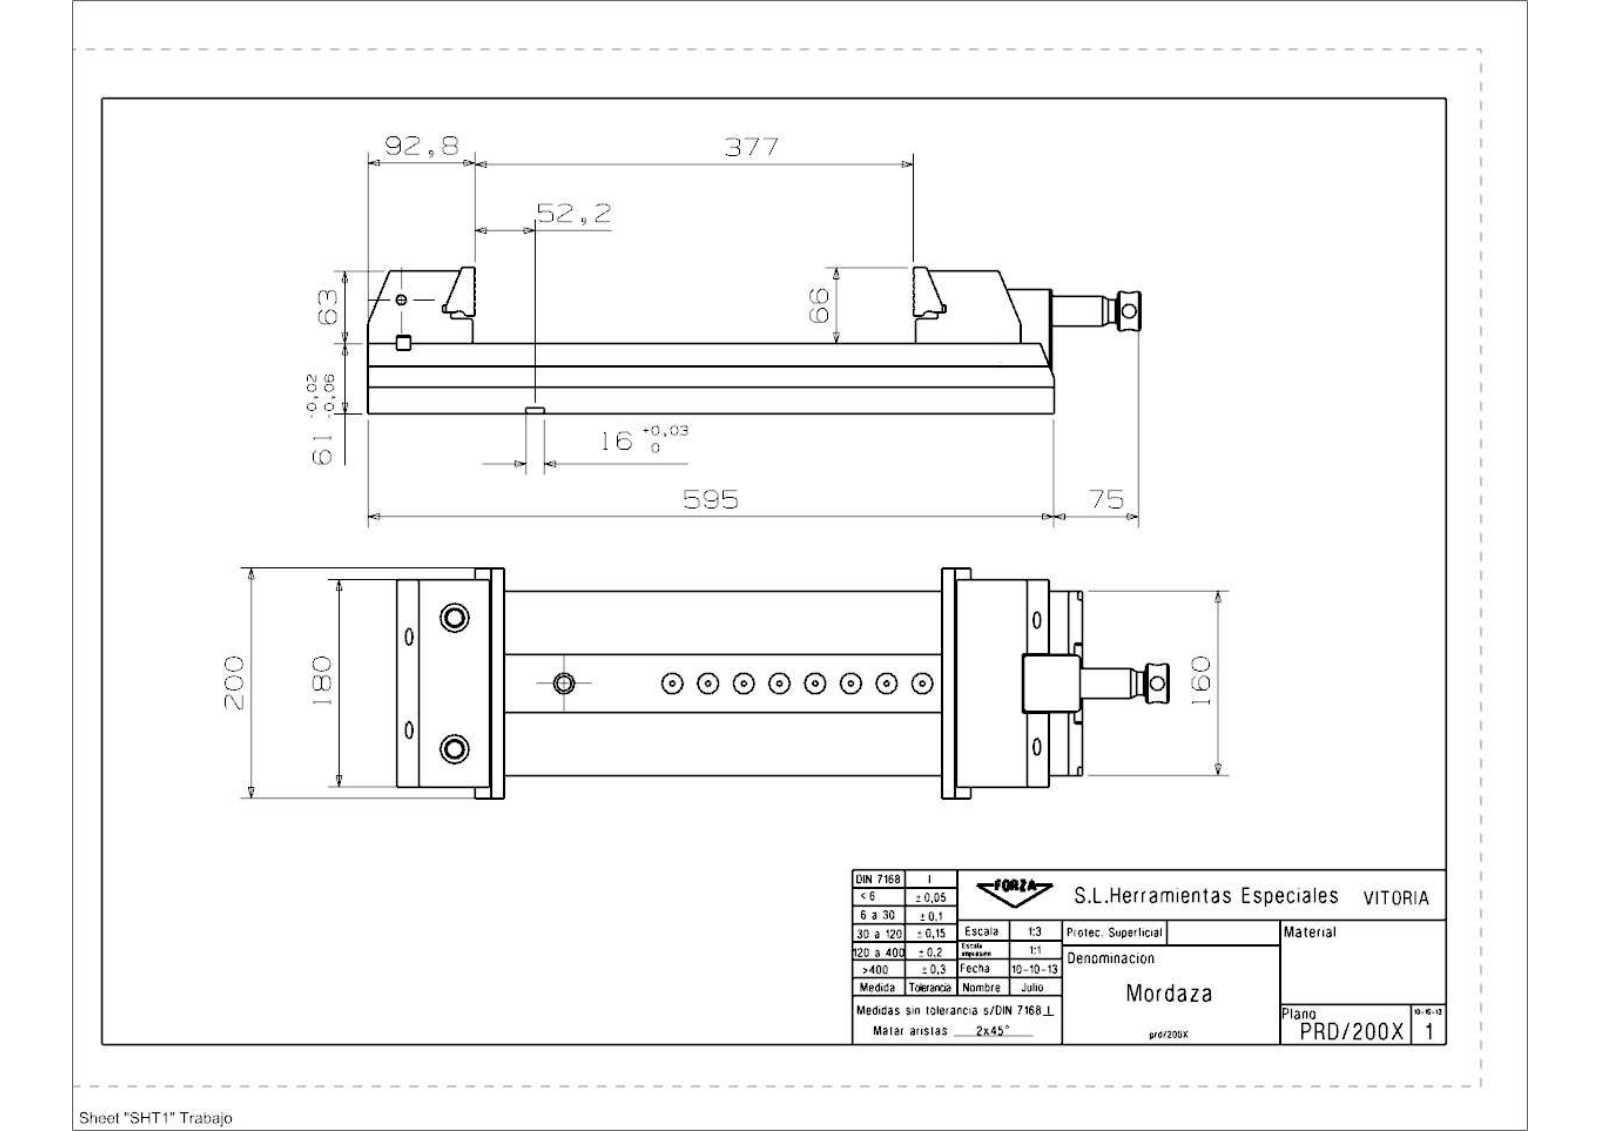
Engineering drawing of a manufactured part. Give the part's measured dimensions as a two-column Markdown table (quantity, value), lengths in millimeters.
| quantity | value |
| --- | --- |
| part name | 30150070 Montaje Taco Hus; PRD_200X_Mordaza |
| STEP written by | SIEMENS PLM Software NX 9.0 (CONFIG_CONTROL_DESIGN) |
| units | millimeters |
| bodies | 11 solids, 470 faces (269 planar, 141 cylindrical, 60 other) |
| overall size | 670 × 200 × 126.95 |
| volume | 6 426 000 mm³ |
| surface area | 666 793 mm² |
| round holes (diameter × count) | 5 × 11, 15 × 6, 5.19 × 5, 13 × 5, 6.99 × 4, 8.5 × 4, 10 × 4, 8.78 × 3, 10.58 × 3, 19 × 3, 12 × 2, 12.38 × 2 |
| round bosses / shafts (diameter × count) | 34 × 1, 33.8 × 1, 26 × 1, 20 × 1, 16.5 × 1 |
| partial cylindrical surfaces (radius × count) | 0.4 × 24, 1.5 × 4, 8 × 4, 20 × 4, 1.6 × 2, 6 × 2, 7 × 2, 4 × 1 |
| main face-to-face distances | 61, 31.8, 29.2, 7.5, 27.2, 2, 59, 160, 63, 152.5 |
| hole center spacings | 31, 62, 93, 14.5, 95.5, 124, 155, 186 |
